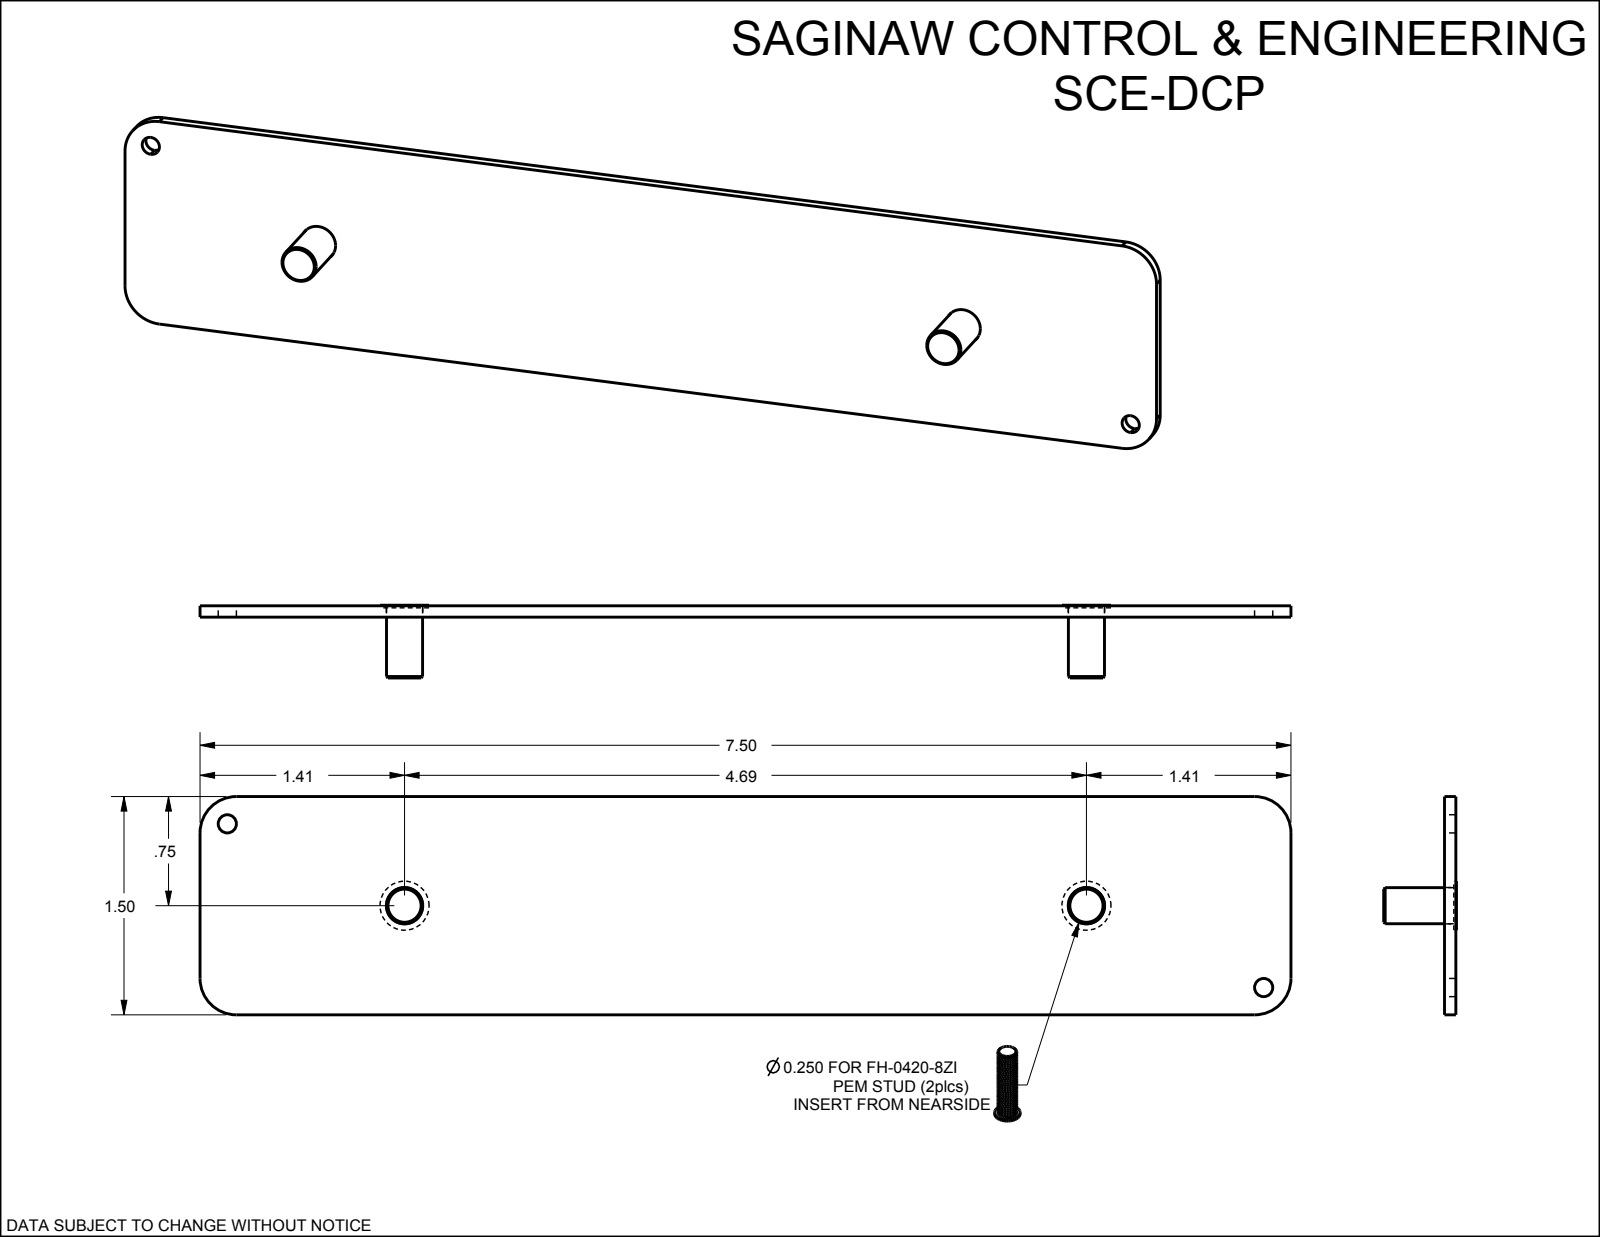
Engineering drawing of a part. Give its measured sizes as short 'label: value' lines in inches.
name: SCE-DCP
written by: SolidWorks 2019 (AUTOMOTIVE_DESIGN)
unit: in
bodies: 3 solids, 26 faces (12 planar, 12 cylindrical, 2 other)
size: 7.5 × 1.5 × 0.5
volume: 0.913 in³; area: 24.84 in²
holes: 2× ⌀0.25, 1× ⌀0.125, 1× ⌀0.125
bosses: 2× ⌀0.337, 2× ⌀0.248
rounds: 4× R0.25
face distances: 0.078, 1.5, 0.082, 0.018, 0.014, 0.064, 0.5, 0.496, 0.482, 0.418
hole spacings: 1.342, 5.933, 4.688, 7.213
